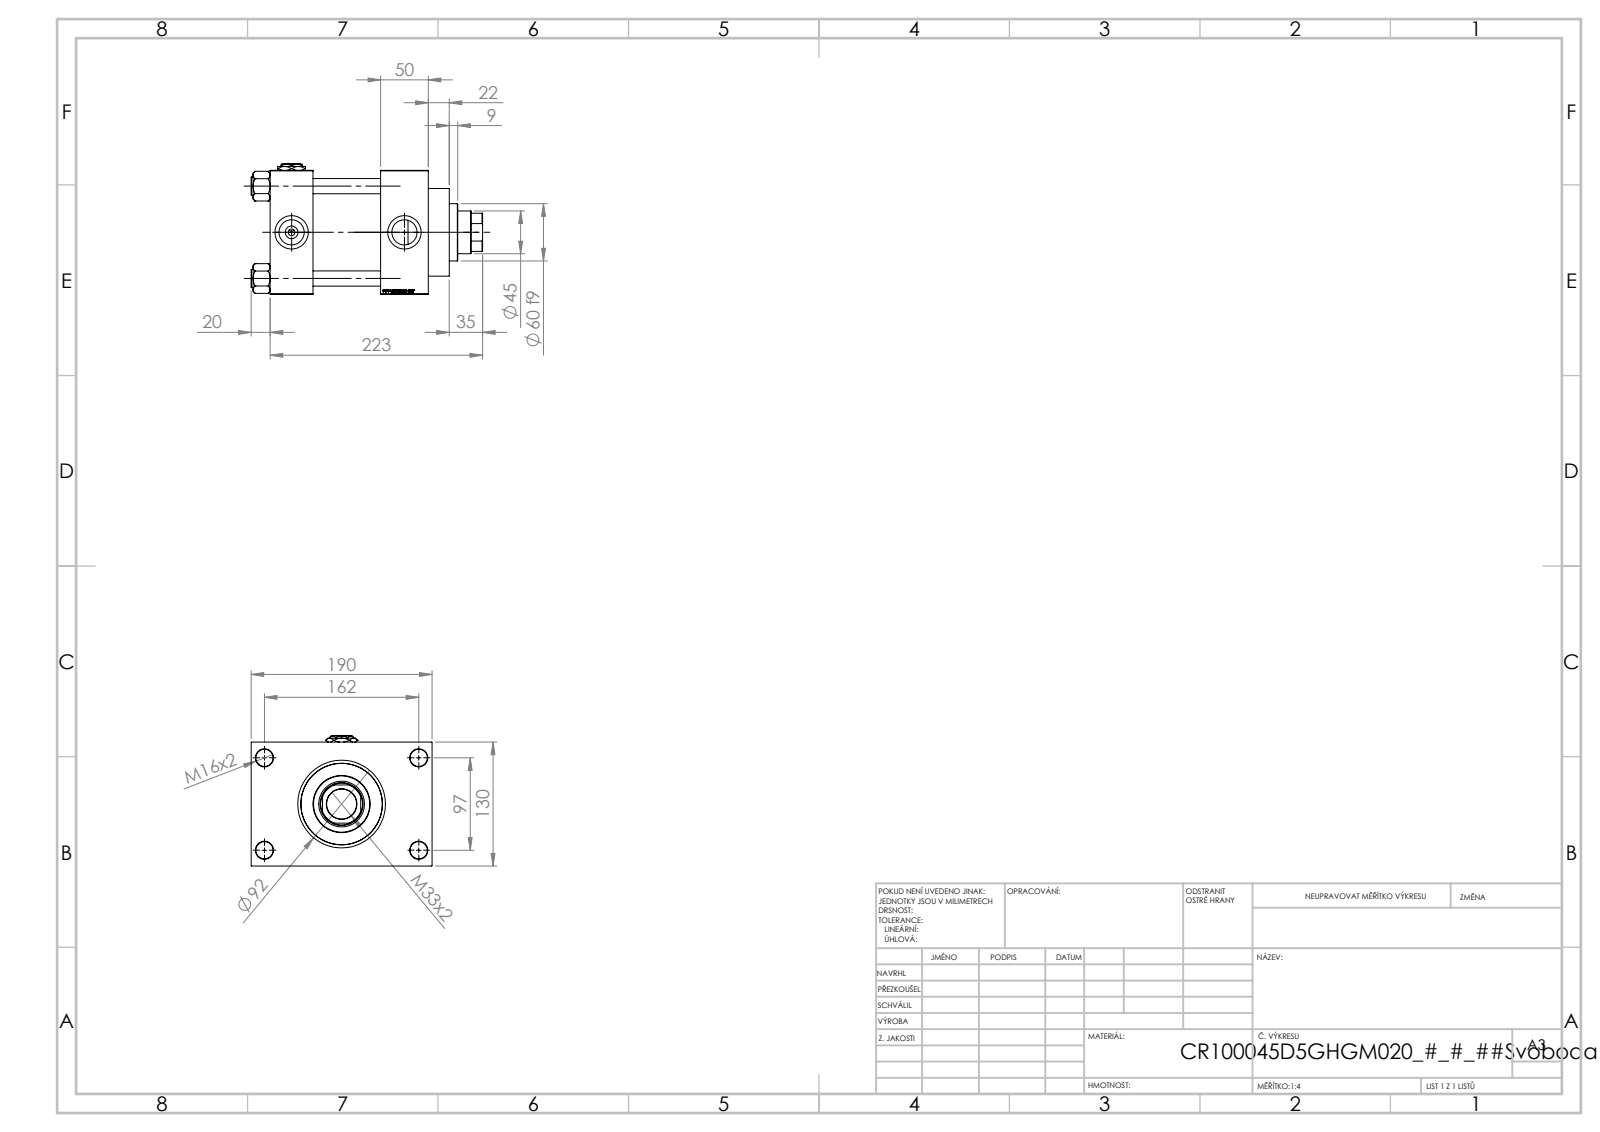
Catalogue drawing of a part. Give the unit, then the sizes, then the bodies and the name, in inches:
Units: inches
Overall size (bounding box): 9.567 × 7.48 × 5.394
Round holes (diameter × count): ⌀0.63 ×4, ⌀0.709 ×4, ⌀0.276 ×3, ⌀1.041 ×3, ⌀1.378 ×3, ⌀1.24 ×1, ⌀1.772 ×1, ⌀1.89 ×1, ⌀2.992 ×1, ⌀3.366 ×1, ⌀3.937 ×1
Round bosses / shafts (diameter × count): ⌀0.748 ×4, ⌀4.173 ×1, ⌀3.622 ×1, ⌀2.362 ×1
Partial cylindrical surfaces — rounded edges, fillets, slot ends (radius × count): R0.866 ×1
Main face-to-face distances: 5.118, 1.772, 4.567, 2.795, 6.535, 4.764, 1.969, 1.181, 6.299, 0.787
Hole centre spacings: 1.281, 2.698, 3.717, 3.815, 4.026, 5.096, 6.367, 3.819
Volume: 157.8 in³ · Surface area: 556.2 in²
Bodies: 12 solids, 1204 faces (569 planar, 95 cylindrical, 540 other)
Part name (STEP PRODUCT): V215_VC_A; V215CR_D_Body; V215CR_D_TYCINKA; V215CR_VCP_D (+2 more)
STEP written by: SolidWorks 2019 (CONFIG_CONTROL_DESIGN)
